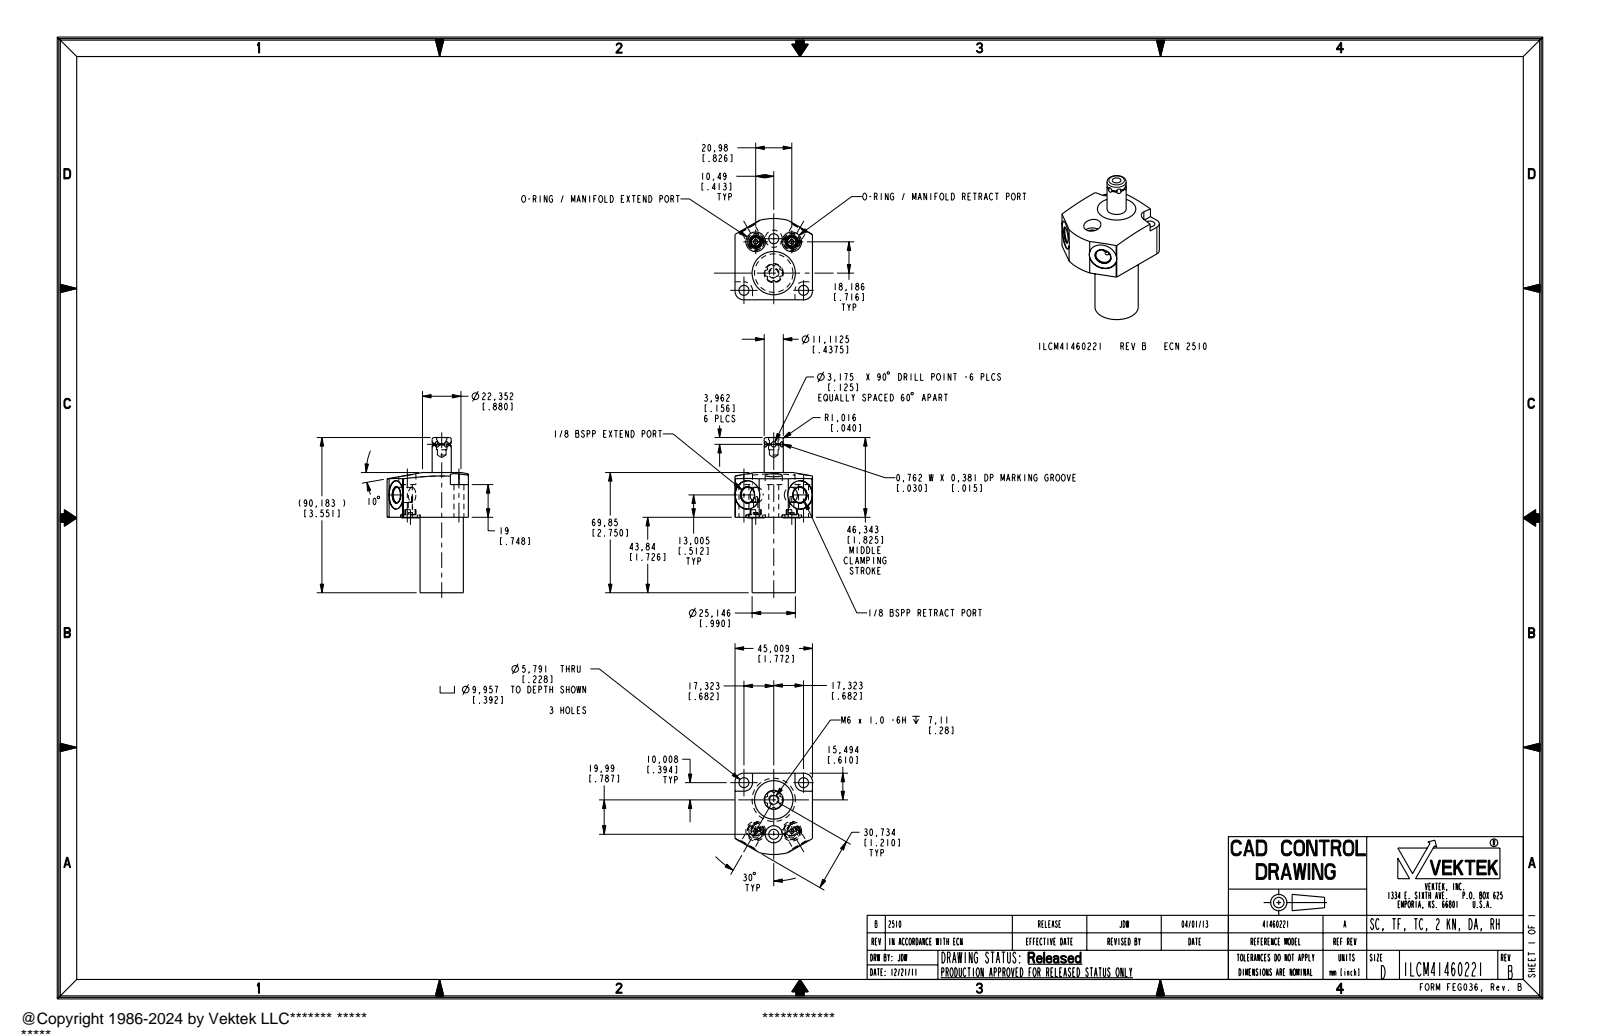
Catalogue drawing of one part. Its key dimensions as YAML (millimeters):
part_name: "ILCM41460221"
step_written_by: "PRO/ENGINEER BY PARAMETRIC TECHNOLOGY CORPORATION, 2007460 (AUTOMOTIVE_DESIGN_CC2)"
units: millimeters
bodies: {solids: 1, faces: 150, planar: 61, cylindrical: 55, other: 34}
overall_size: [90.18, 47.24, 45.01]
volume: 67421
surface_area: 14752
round_holes:
  - {diameter: 5.79, count: 3}
  - {diameter: 2.49, count: 2}
  - {diameter: 6.5, count: 2}
  - {diameter: 8.84, count: 2}
  - {diameter: 11.4, count: 2}
  - {diameter: 16.51, count: 2}
  - {diameter: 5.05, count: 1}
  - {diameter: 9.96, count: 1}
round_bosses_or_shafts:
  - {diameter: 5.49, count: 2}
  - {diameter: 25.15, count: 1}
  - {diameter: 11.11, count: 1}
  - {diameter: 5.99, count: 1}
partial_cylinders:
  - {radius: 4.9, count: 2}
  - {radius: 4.98, count: 2}
  - {radius: 5.17, count: 1}
  - {radius: 31.75, count: 1}
face_to_face_distances: [45, 43.84, 69.85, 26.01, 62.84, 19, 7.01, 45.29, 1.45, 17.55]
hole_center_spacings: [34.64, 10.64, 20, 21, 29.02, 39.61, 19.99, 20.98]
